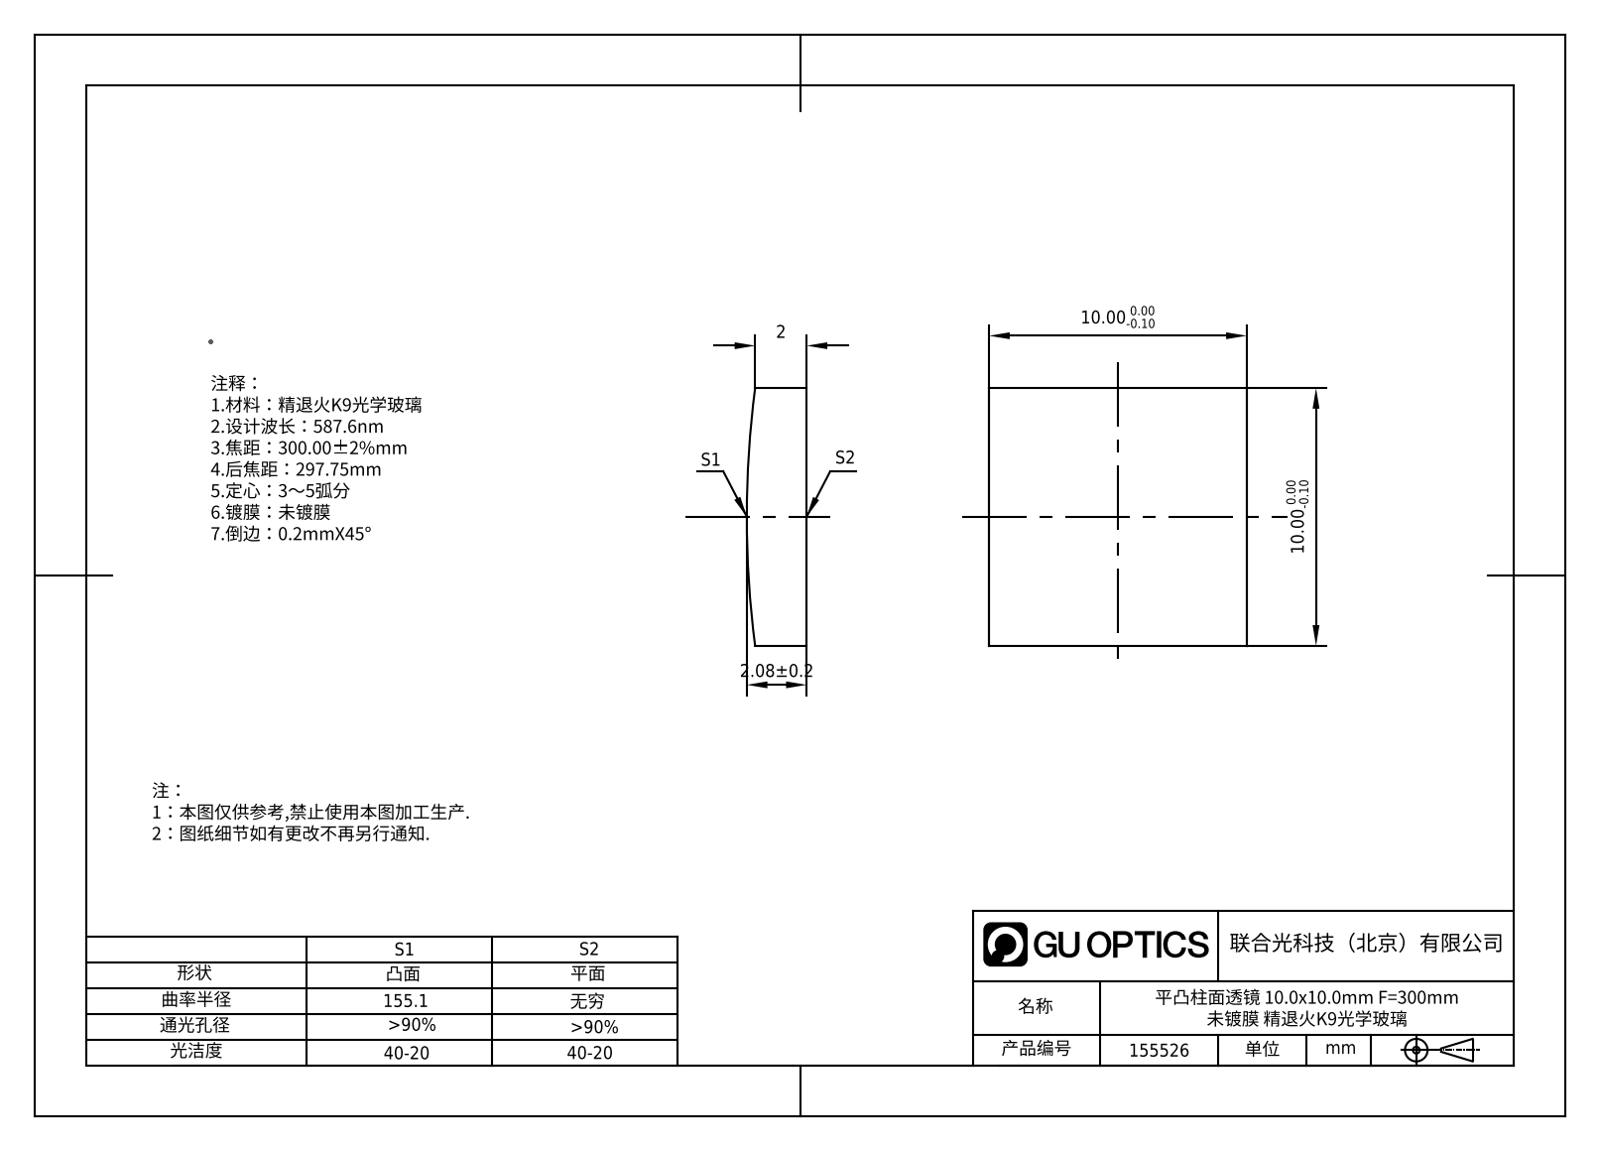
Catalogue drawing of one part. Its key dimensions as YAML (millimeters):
part_name: "155526"
step_written_by: "SolidWorks 2020 (CONFIG_CONTROL_DESIGN)"
units: millimeters
bodies: {solids: 1, faces: 7, planar: 5, cylindrical: 2, other: 0}
overall_size: [10, 10, 2.08]
volume: 205
surface_area: 281
partial_cylinders:
  - {radius: 155.1, count: 1}
face_to_face_distances: [10]
